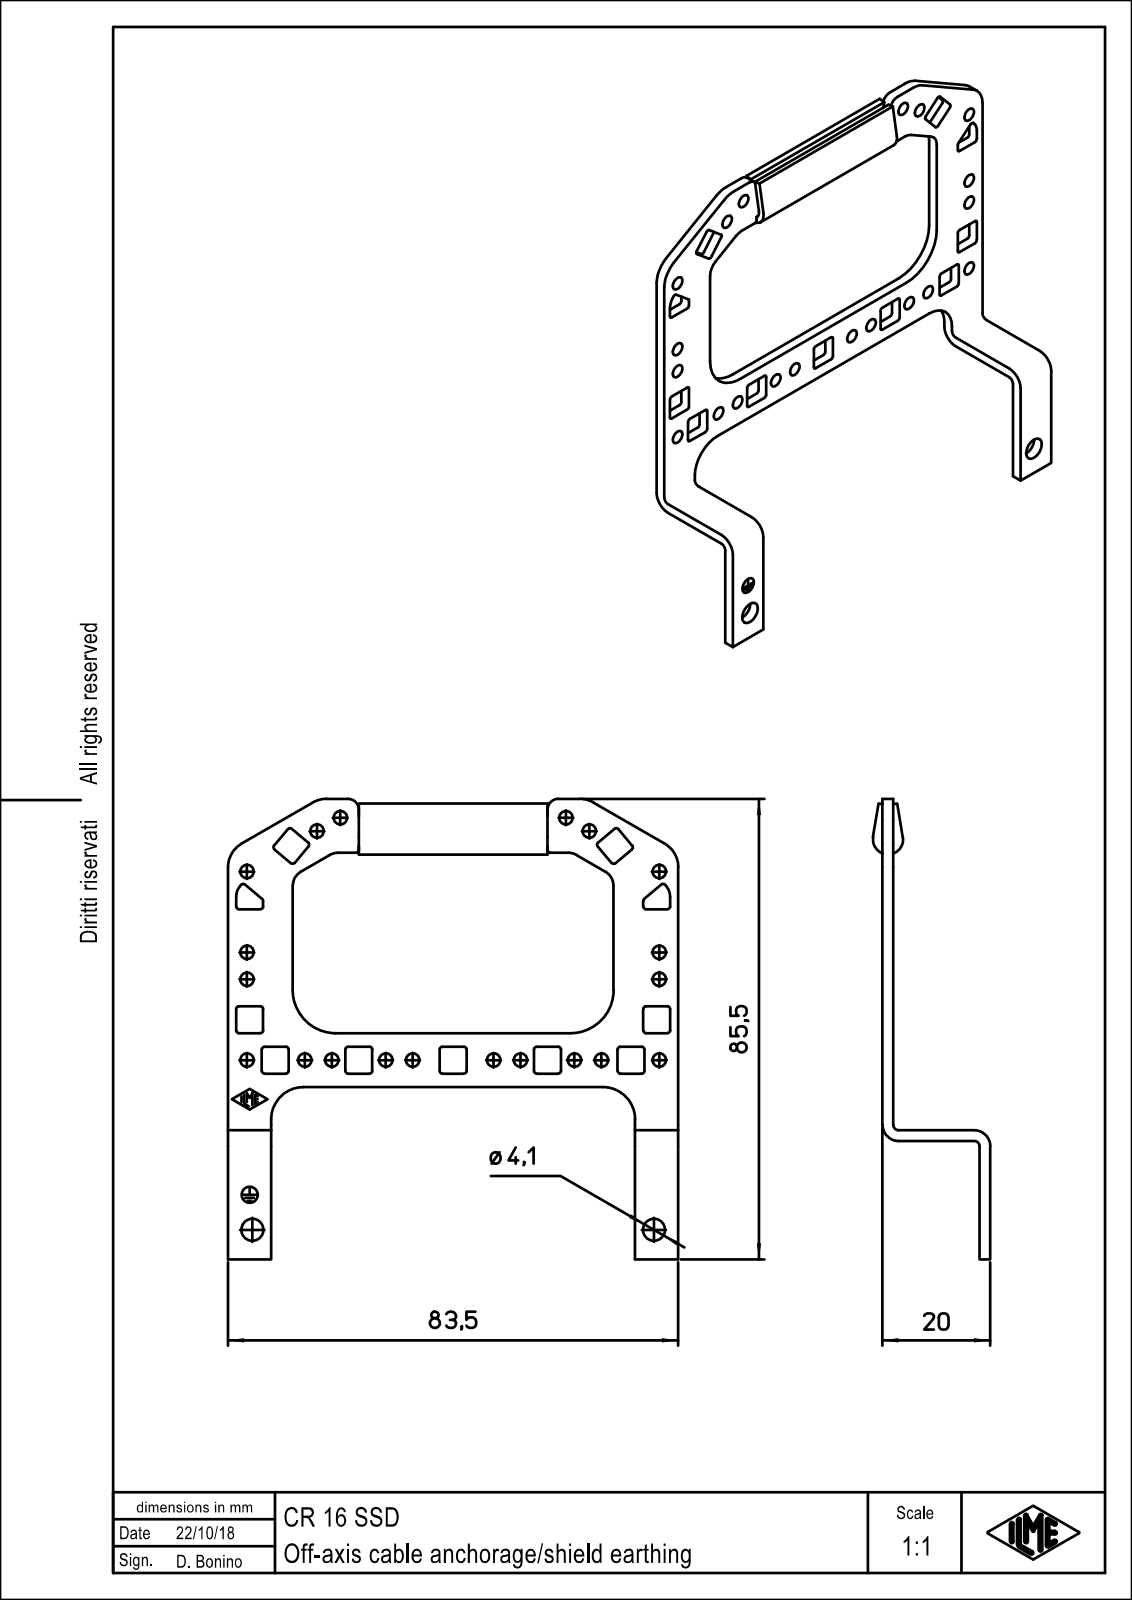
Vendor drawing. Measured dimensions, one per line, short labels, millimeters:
name: CR_16_SSD
written by: PTC Creo Elements/Direct Modeling 19.0B 21-Mar-2015 (C) Parametric Technology GmbH (AUTOMOTIVE_DESIGN)
unit: mm
bodies: 1 solid, 169 faces (100 planar, 69 cylindrical, 0 other)
size: 85.5 × 83.5 × 21.8
volume: 6 441 mm³; area: 7 745 mm²
holes: 20× ⌀2.5, 2× ⌀4.1, 1× ⌀3
bosses: 1× ⌀2.7
rounds: 6× R3, 4× R5, 2× R1, 2× R6, 2× R8, 1× R2.8
face distances: 2, 18, 20, 16, 8, 10, 63.5, 75.5, 83.5, 5
hole spacings: 15, 20, 5, 35, 30.41, 76.5, 77.96, 79.07
